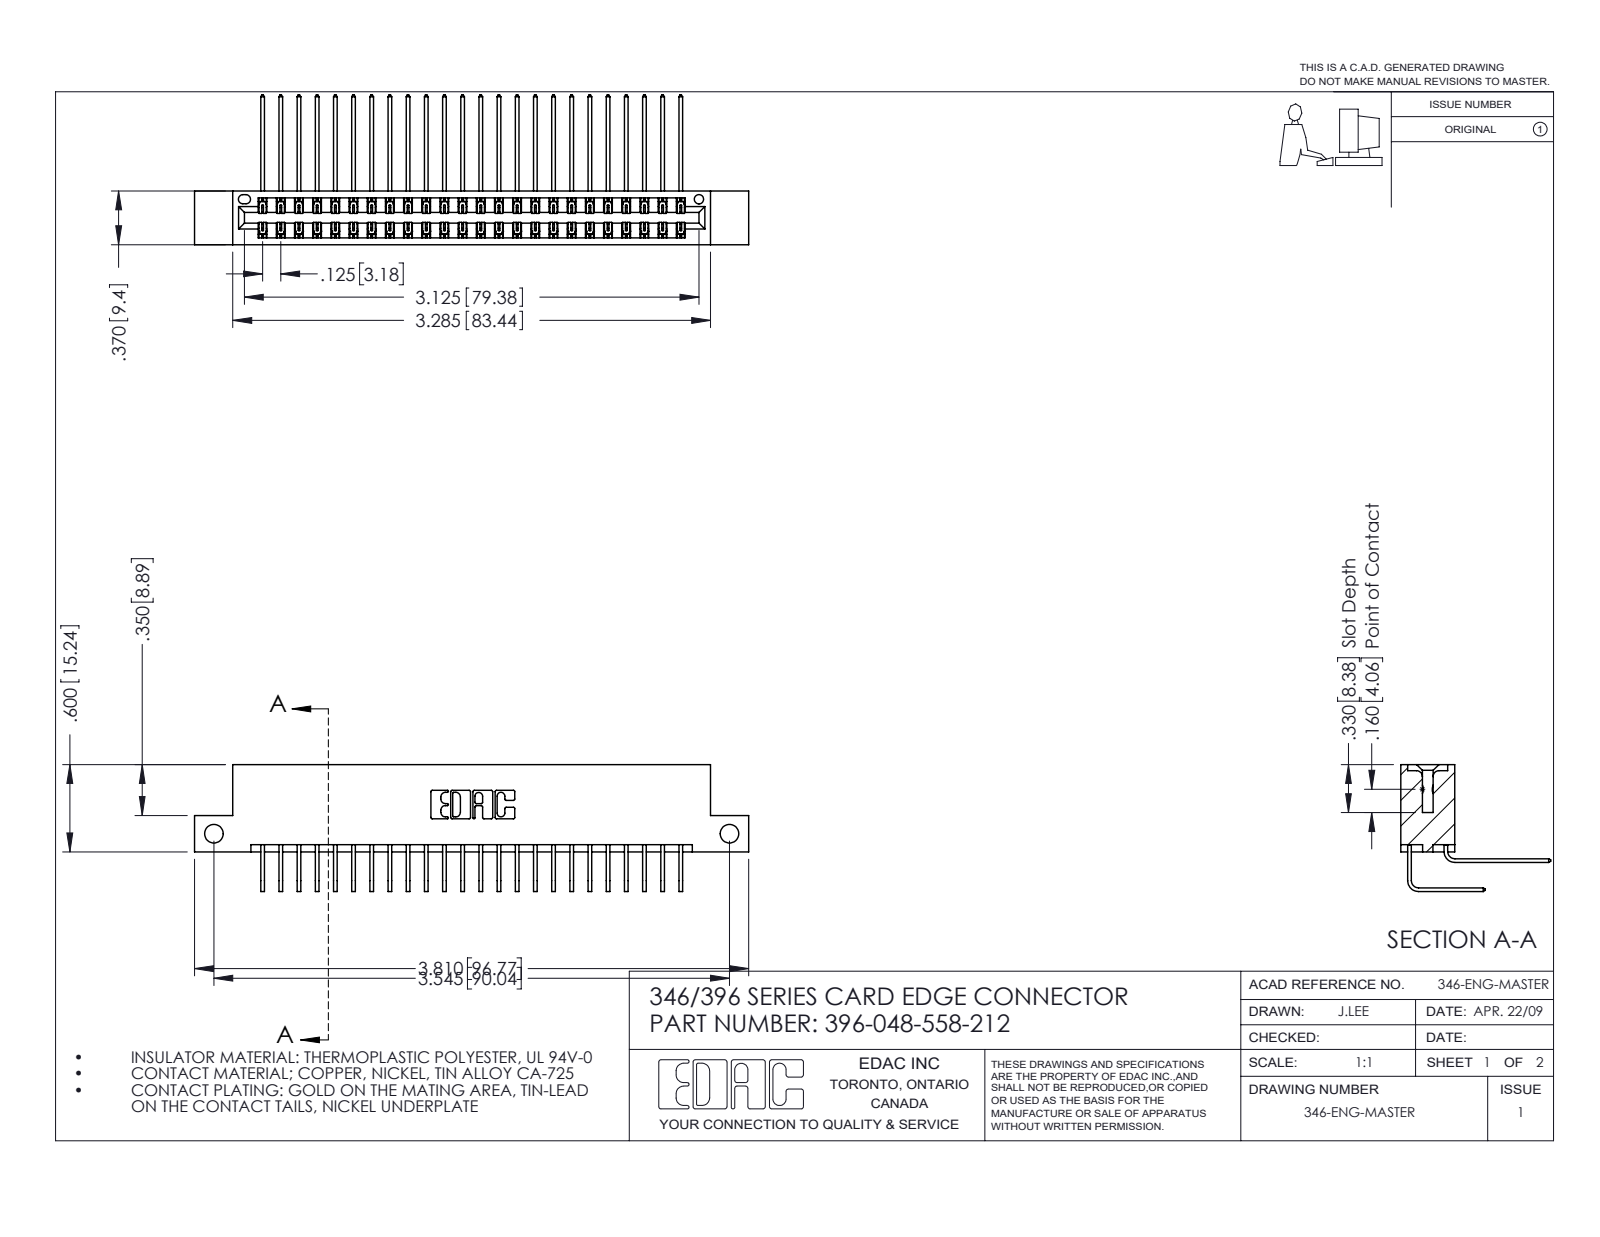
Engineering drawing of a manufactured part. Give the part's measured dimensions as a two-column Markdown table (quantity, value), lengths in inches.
| quantity | value |
| --- | --- |
| part name | 345-292-001_558 Tail - 2; 396-048-558-212; 345-292-001_558 559 Tail - 1; 346 Part_Flush Mounting Lugs - Side Mount |
| STEP written by | SolidWorks 2016 (CONFIG_CONTROL_DESIGN) |
| units | inches |
| bodies | 49 solids, 2714 faces (1852 planar, 862 cylindrical, 0 other) |
| overall size | 3.81 × 1.03 × 0.873 |
| volume | 0.579 in³ |
| surface area | 21.62 in² |
| round holes (diameter × count) | 0.128 × 2, 0.064 × 1 |
| partial cylindrical surfaces (radius × count) | 0.006 × 72, 0.01 × 22, 0.007 × 6, 0.031 × 6, 0.026 × 3, 0.014 × 2, 0.022 × 2, 0.024 × 2 |
| main face-to-face distances | 0.322, 0.048, 0.25, 0.025, 0.37, 0.298, 0.072, 0.275, 0.148, 0.222 |
| hole center spacings | 3.545 |
